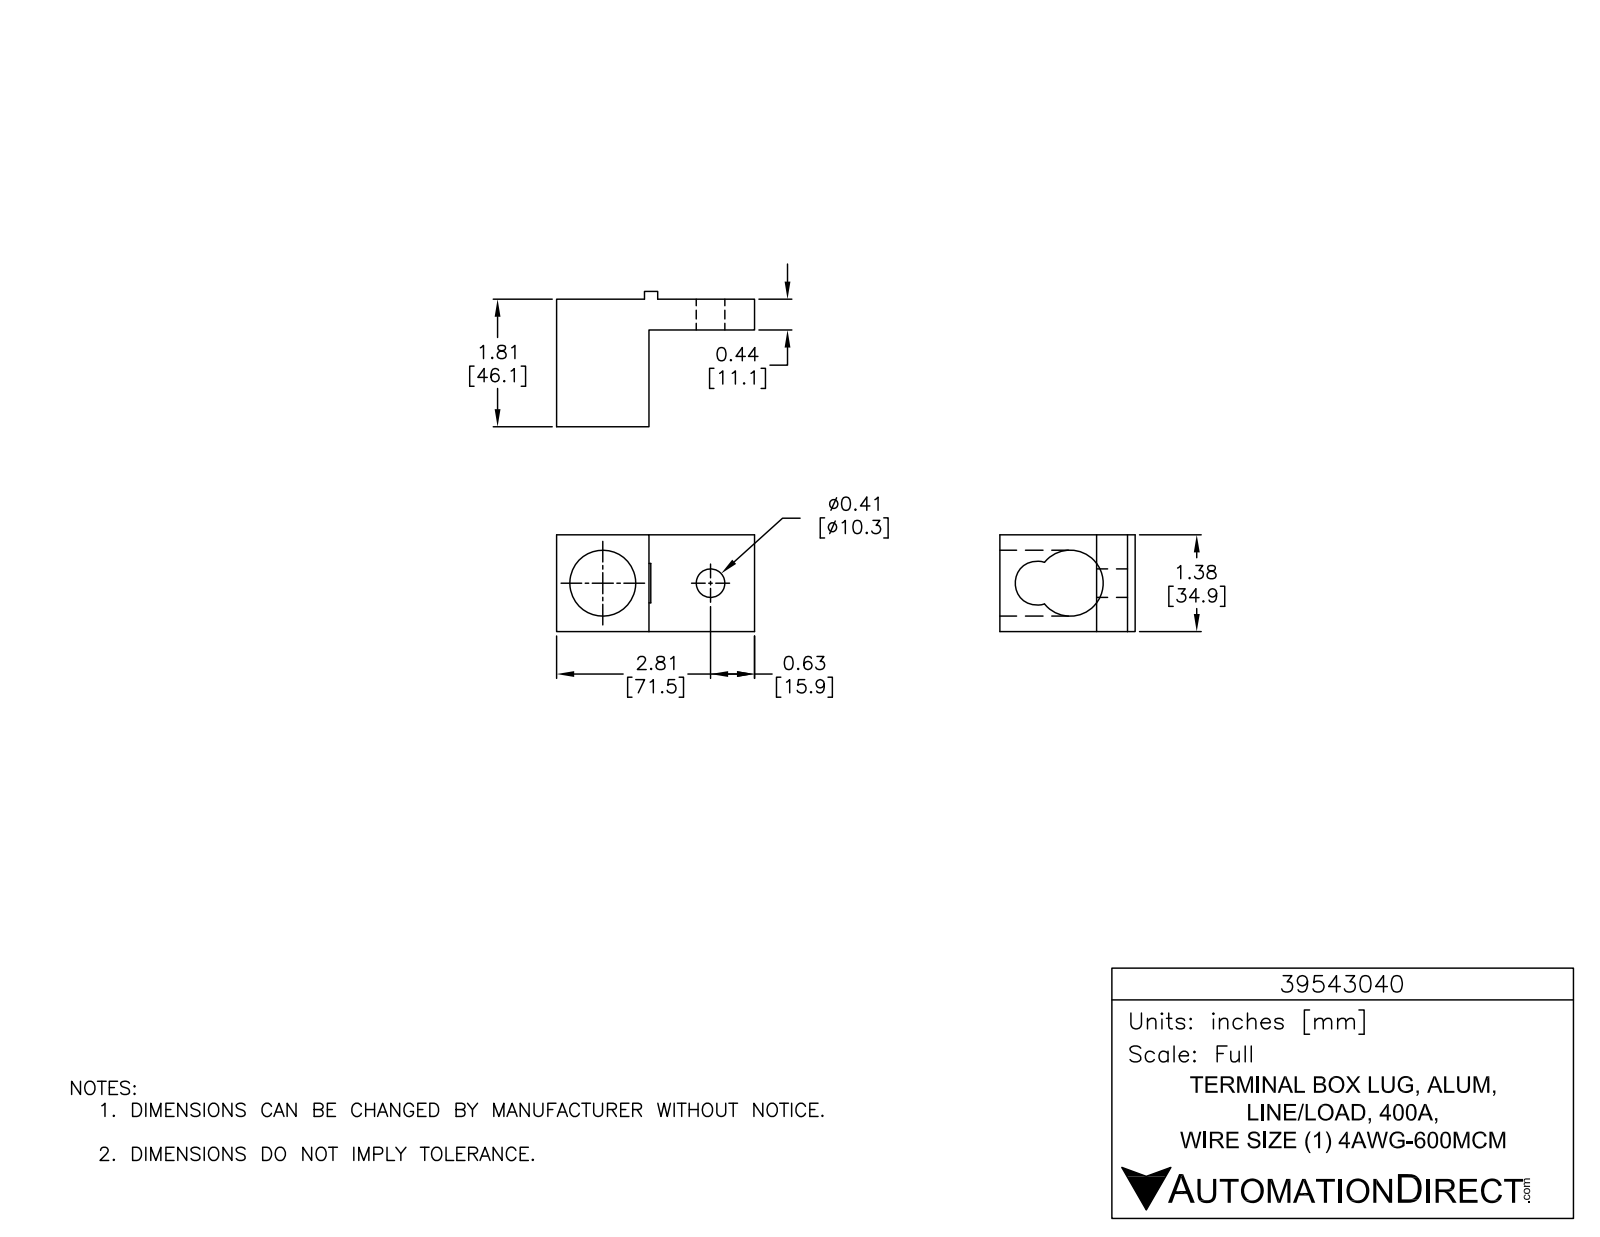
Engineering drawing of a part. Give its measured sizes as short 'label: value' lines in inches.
name: 39543040
written by: SolidWorks 2015 (AUTOMOTIVE_DESIGN)
unit: in
bodies: 1 solid, 22 faces (13 planar, 9 cylindrical, 0 other)
size: 2.813 × 1.922 × 1.375
volume: 2.749 in³; area: 22.08 in²
holes: 1× ⌀0.406, 1× ⌀0.937
rounds: 1× R0.313, 1× R0.469
face distances: 1.375, 0.438, 1.813, 1.375, 1.313, 2.813, 1.5, 0.109, 0.547, 1.922
hole spacings: 1.531
